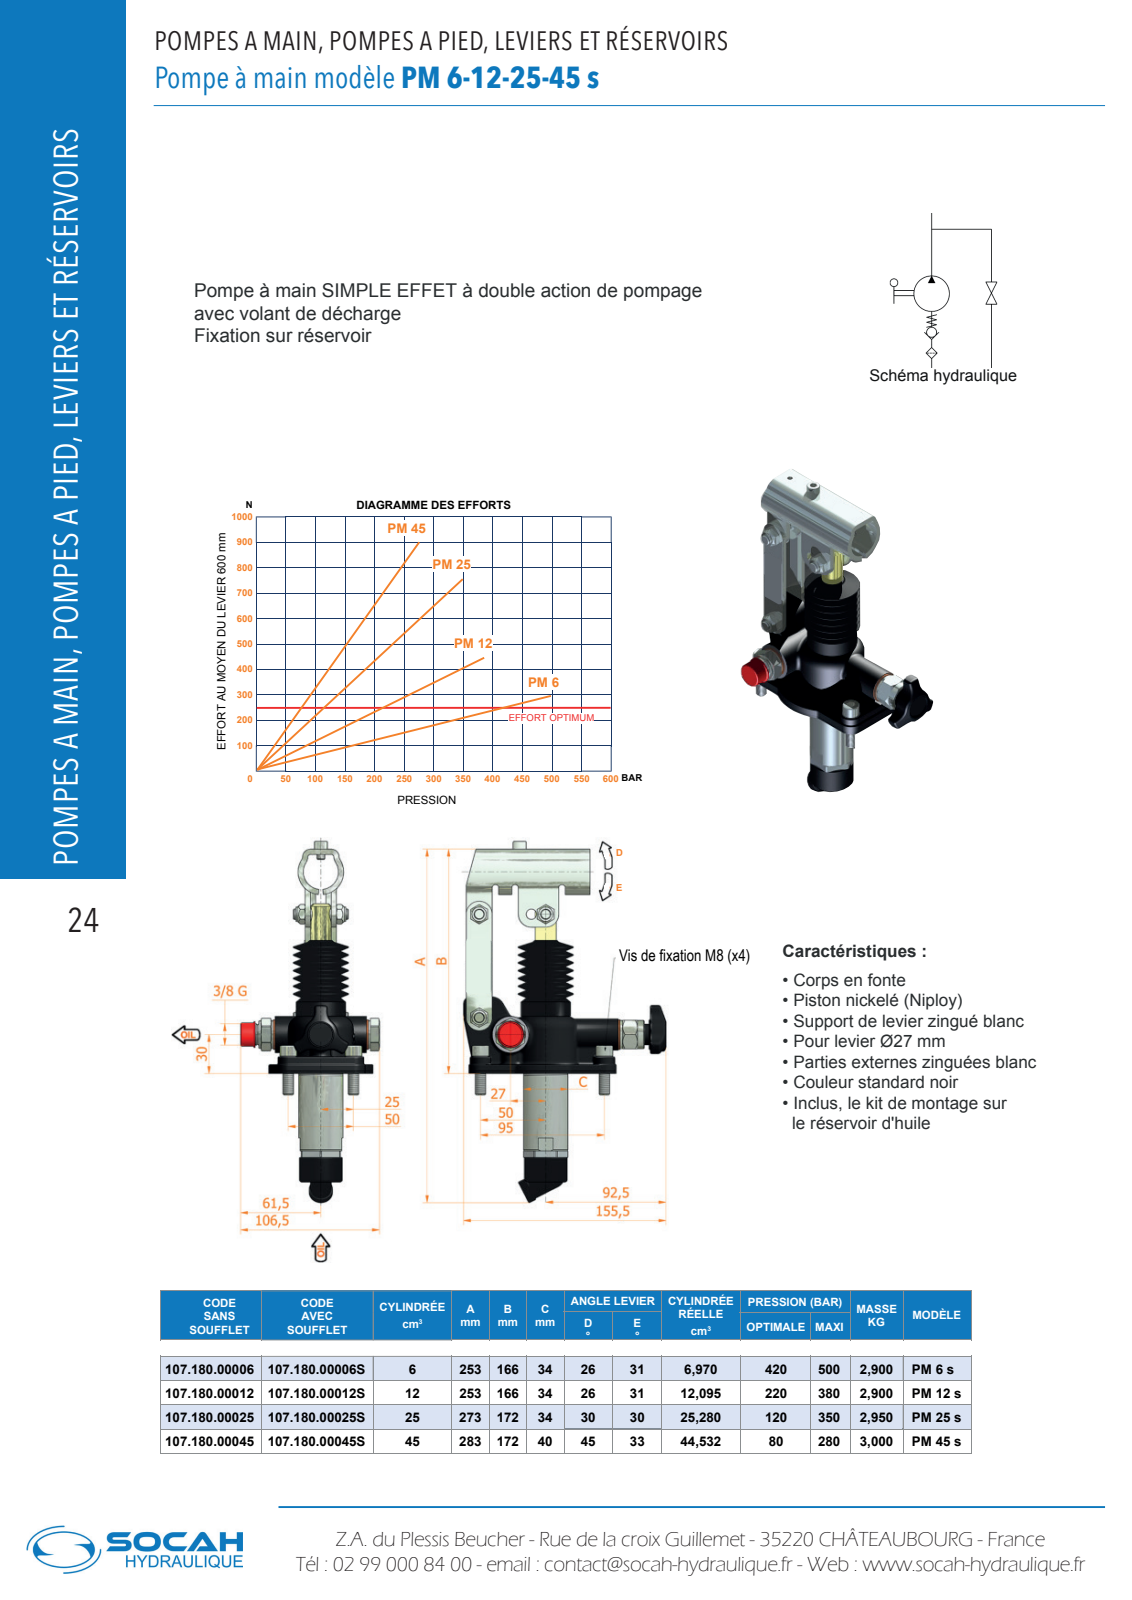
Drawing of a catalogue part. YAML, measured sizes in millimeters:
part_name: "6051.0116.00.50 Derivazione 2"
step_written_by: "Autodesk Inventor 2013 (AUTOMOTIVE_DESIGN)"
units: millimeters
bodies: {solids: 12, faces: 1540, planar: 699, cylindrical: 350, other: 491}
overall_size: [277.85, 155.22, 106.5]
volume: 267032
surface_area: 140720
round_holes:
  - {diameter: 8, count: 6}
  - {diameter: 14, count: 4}
  - {diameter: 10, count: 2}
  - {diameter: 4, count: 1}
  - {diameter: 5, count: 1}
  - {diameter: 9, count: 1}
  - {diameter: 17, count: 1}
  - {diameter: 18, count: 1}
  - {diameter: 21, count: 1}
  - {diameter: 22, count: 1}
  - {diameter: 25, count: 1}
  - {diameter: 29, count: 1}
round_bosses_or_shafts:
  - {diameter: 13, count: 4}
  - {diameter: 12, count: 4}
  - {diameter: 8.5, count: 4}
  - {diameter: 18, count: 3}
  - {diameter: 16, count: 3}
  - {diameter: 11.05, count: 3}
  - {diameter: 8, count: 3}
  - {diameter: 23, count: 2}
partial_cylinders:
  - {radius: 1, count: 31}
  - {radius: 0.2, count: 24}
  - {radius: 2, count: 22}
  - {radius: 3, count: 17}
  - {radius: 0.1, count: 16}
  - {radius: 10, count: 10}
  - {radius: 8, count: 9}
  - {radius: 0.36, count: 6}
face_to_face_distances: [4, 20, 16, 2, 5, 7, 1, 24, 13, 165.5]
hole_center_spacings: [25.5, 26.1, 26.93, 50, 51.48, 55.9, 88.6, 91]
